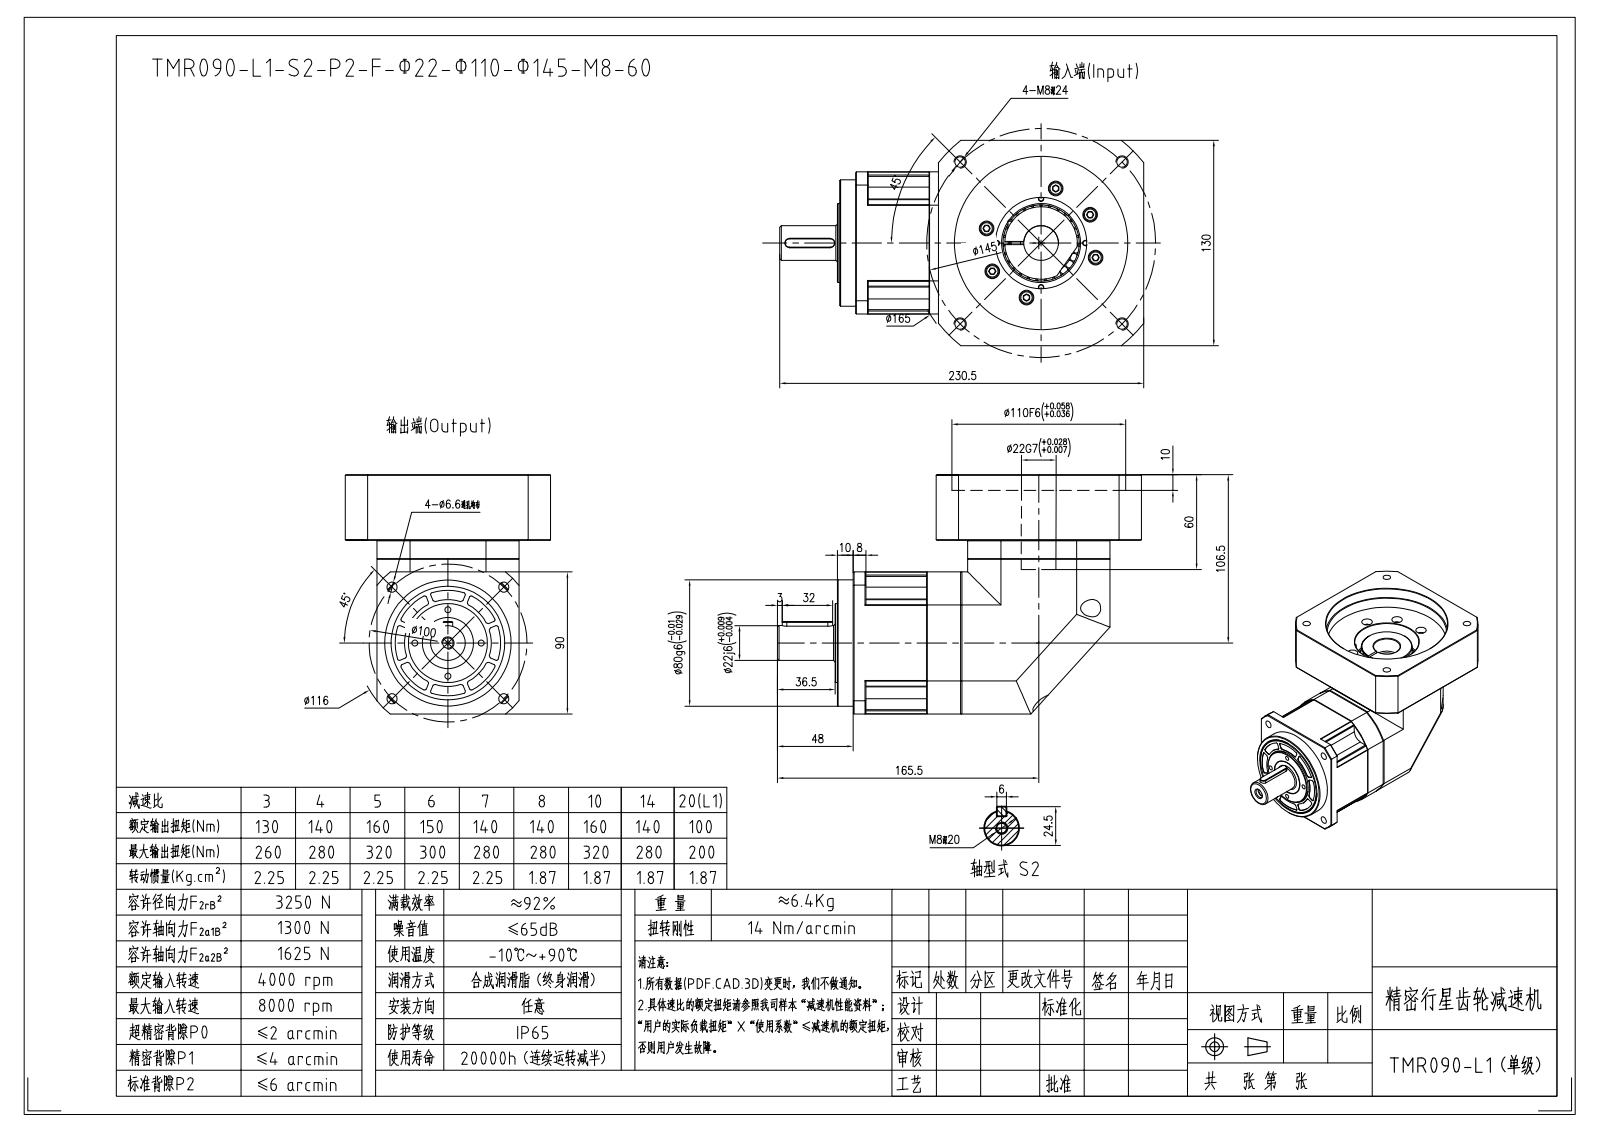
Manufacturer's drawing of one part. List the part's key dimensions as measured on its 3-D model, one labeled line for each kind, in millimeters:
Part name (STEP PRODUCT): HEXAGON_SOCKET_HEAD_CAP_S-14123; 40X50X500; HEXAGON_SOCKET_HEAD_CAP_S-14176; TMR900003 (+8 more)
STEP written by: CREO PARAMETRIC BY PTC INC, 2020053 (CONFIG_CONTROL_DESIGN)
Units: millimetres
Bodies: 42 solids, 1256 faces (505 planar, 534 cylindrical, 217 other)
Overall size (bounding box): 230.5 × 151.5 × 130
Volume: 1 639 000 mm³ · Surface area: 245 612 mm²
Round holes (diameter × count): ⌀5.4 ×12, ⌀9.5 ×12, ⌀4.2 ×7, ⌀5.5 ×6, ⌀6.5 ×5, ⌀6.8 ×5, ⌀4 ×4, ⌀6.6 ×4, ⌀6.68 ×4, ⌀11 ×4, ⌀5 ×1, ⌀8.4 ×1
Round bosses / shafts (diameter × count): ⌀8.5 ×12, ⌀8 ×12, ⌀5 ×12, ⌀10 ×4, ⌀9.88 ×4, ⌀6 ×4, ⌀80 ×1, ⌀55 ×1
Partial cylindrical surfaces — rounded edges, fillets, slot ends (radius × count): R1 ×92, R7.5 ×4, R51 ×3, R3 ×2, R4 ×1, R5.25 ×1, R50.25 ×1, R58 ×1
Main face-to-face distances: 20, 110, 21.5, 41.5, 90, 12, 21.3, 130, 53.5, 5
Hole centre spacings: 35.75, 27.36, 38.16, 66.06, 66.53, 88.75, 39.08, 61.92
